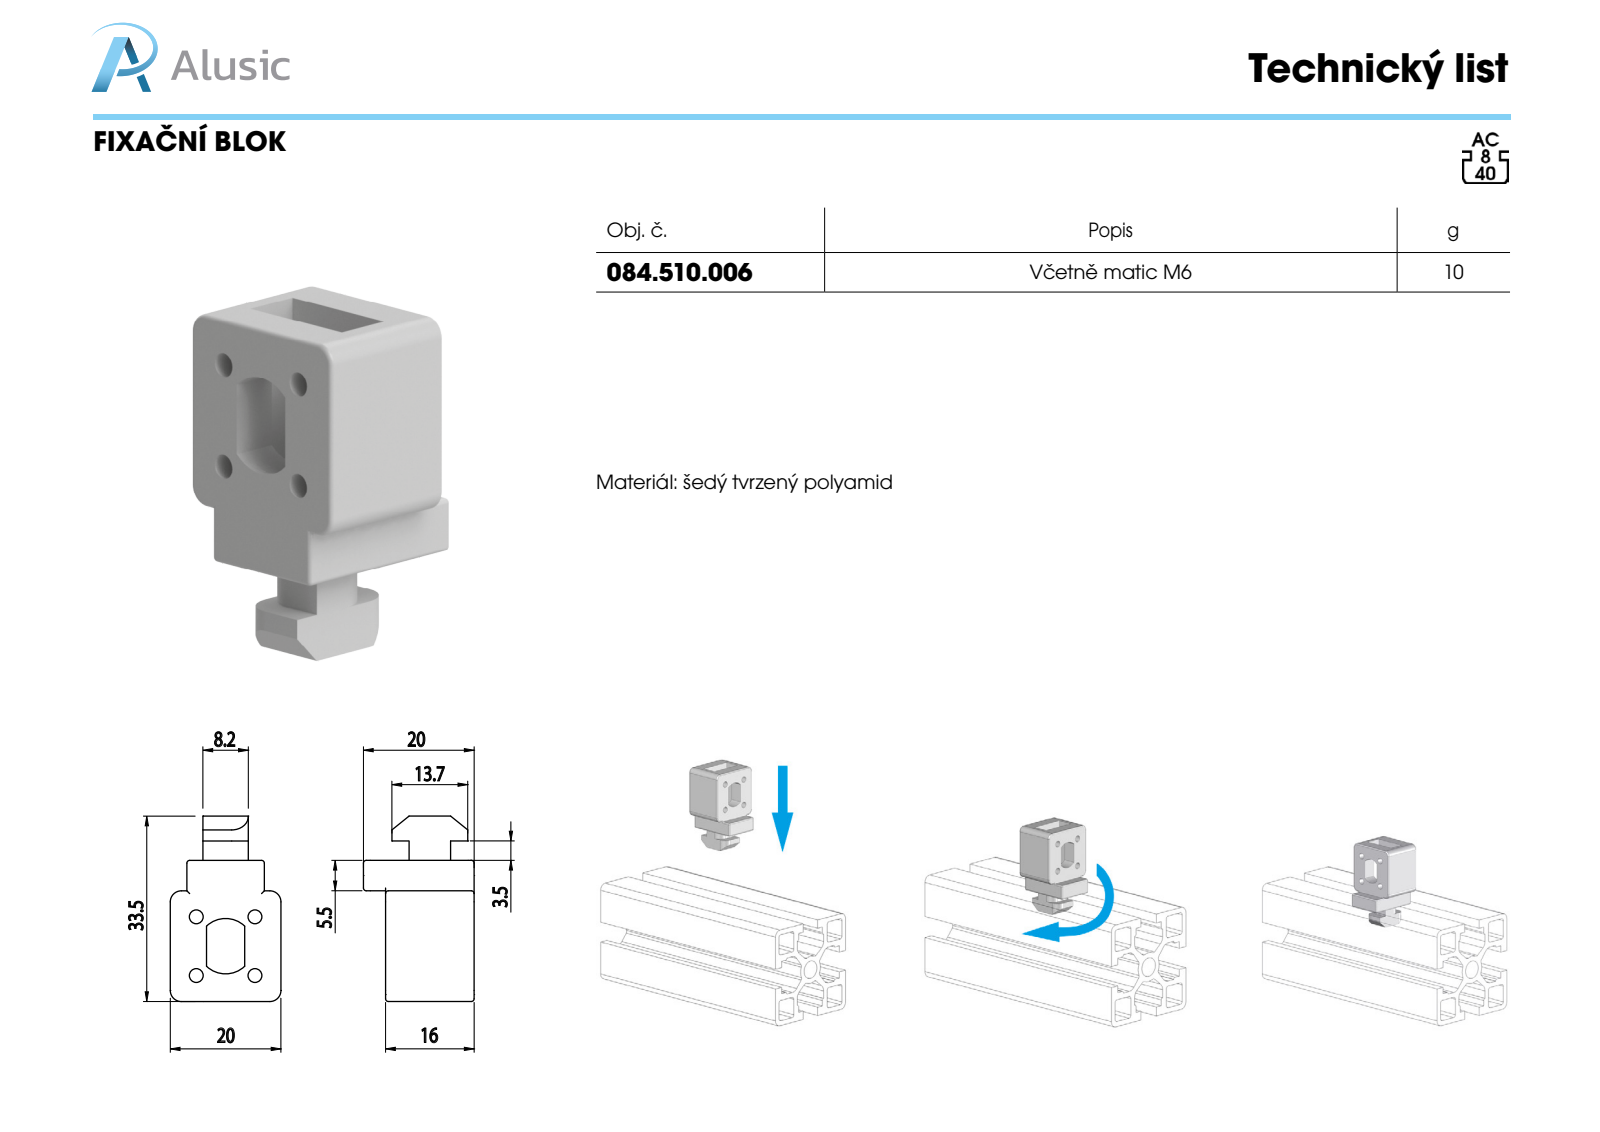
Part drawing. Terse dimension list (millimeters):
name: 084.510.006-1
written by: SolidWorks 2011 (CONFIG_CONTROL_DESIGN)
unit: mm
bodies: 1 solid, 103 faces (40 planar, 49 cylindrical, 14 other)
size: 33.5 × 20 × 20
volume: 6 471 mm³; area: 3 666 mm²
holes: 4× ⌀2.5
rounds: 19× R0.5, 4× R2, 4× R3, 1× R5
face distances: 20, 3.5, 5, 11, 16, 16.5, 17, 13.5, 3, 9
hole spacings: 10.6, 14.99
